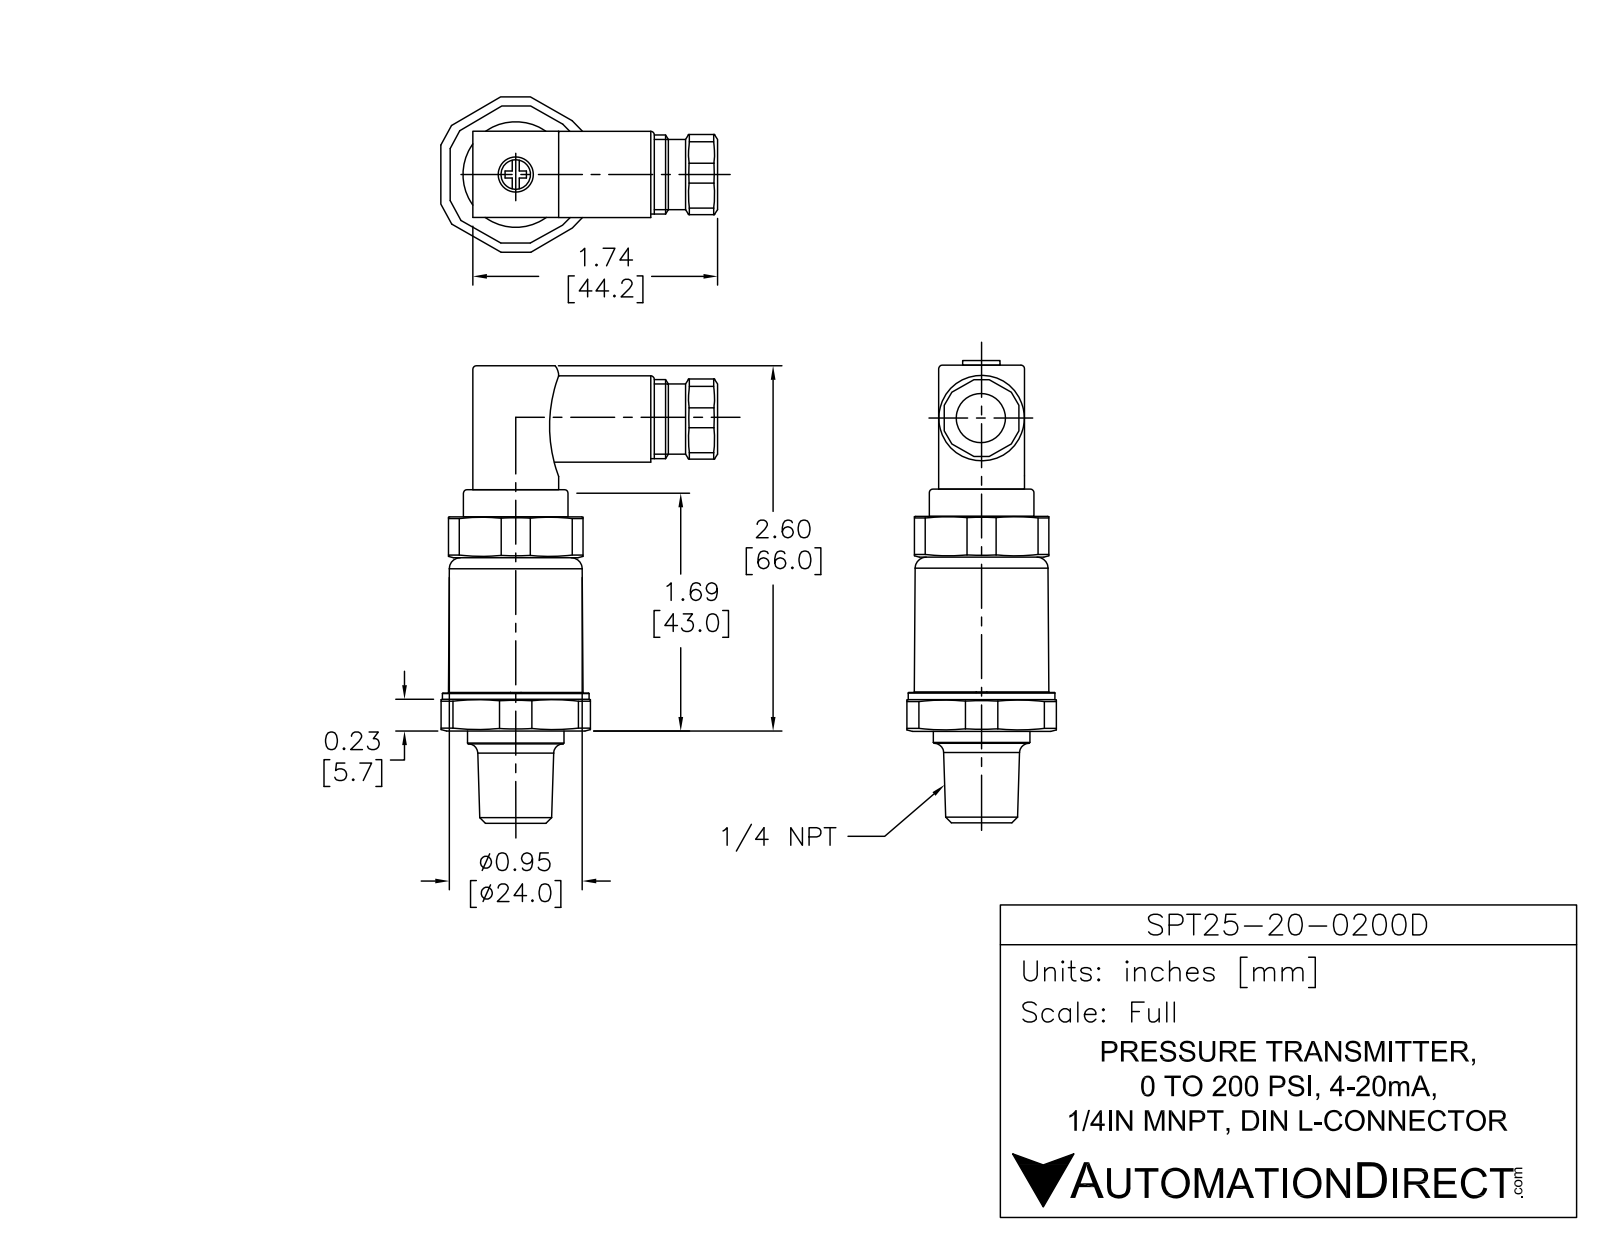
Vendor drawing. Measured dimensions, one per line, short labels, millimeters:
name: SPT25-20-0200D
written by: SolidWorks 2011 (AUTOMOTIVE_DESIGN)
unit: mm
bodies: 5 solids, 170 faces (96 planar, 64 cylindrical, 10 other)
size: 81.25 × 38.01 × 35.71
volume: 27 900 mm³; area: 10 134 mm²
holes: 1× ⌀1, 1× ⌀3.3, 1× ⌀7, 1× ⌀8
bosses: 1× ⌀26.75, 1× ⌀24, 1× ⌀17.5, 1× ⌀15, 1× ⌀14, 1× ⌀11
rounds: 8× R1.5, 4× R1.15, 4× R2.25, 3× R2, 1× R1.15, 1× R1.17, 1× R14.5
face distances: 1.5, 29.5, 31, 15.75, 0.35, 15.4, 6.75, 37.75, 36.25, 5
hole spacings: 1.33
